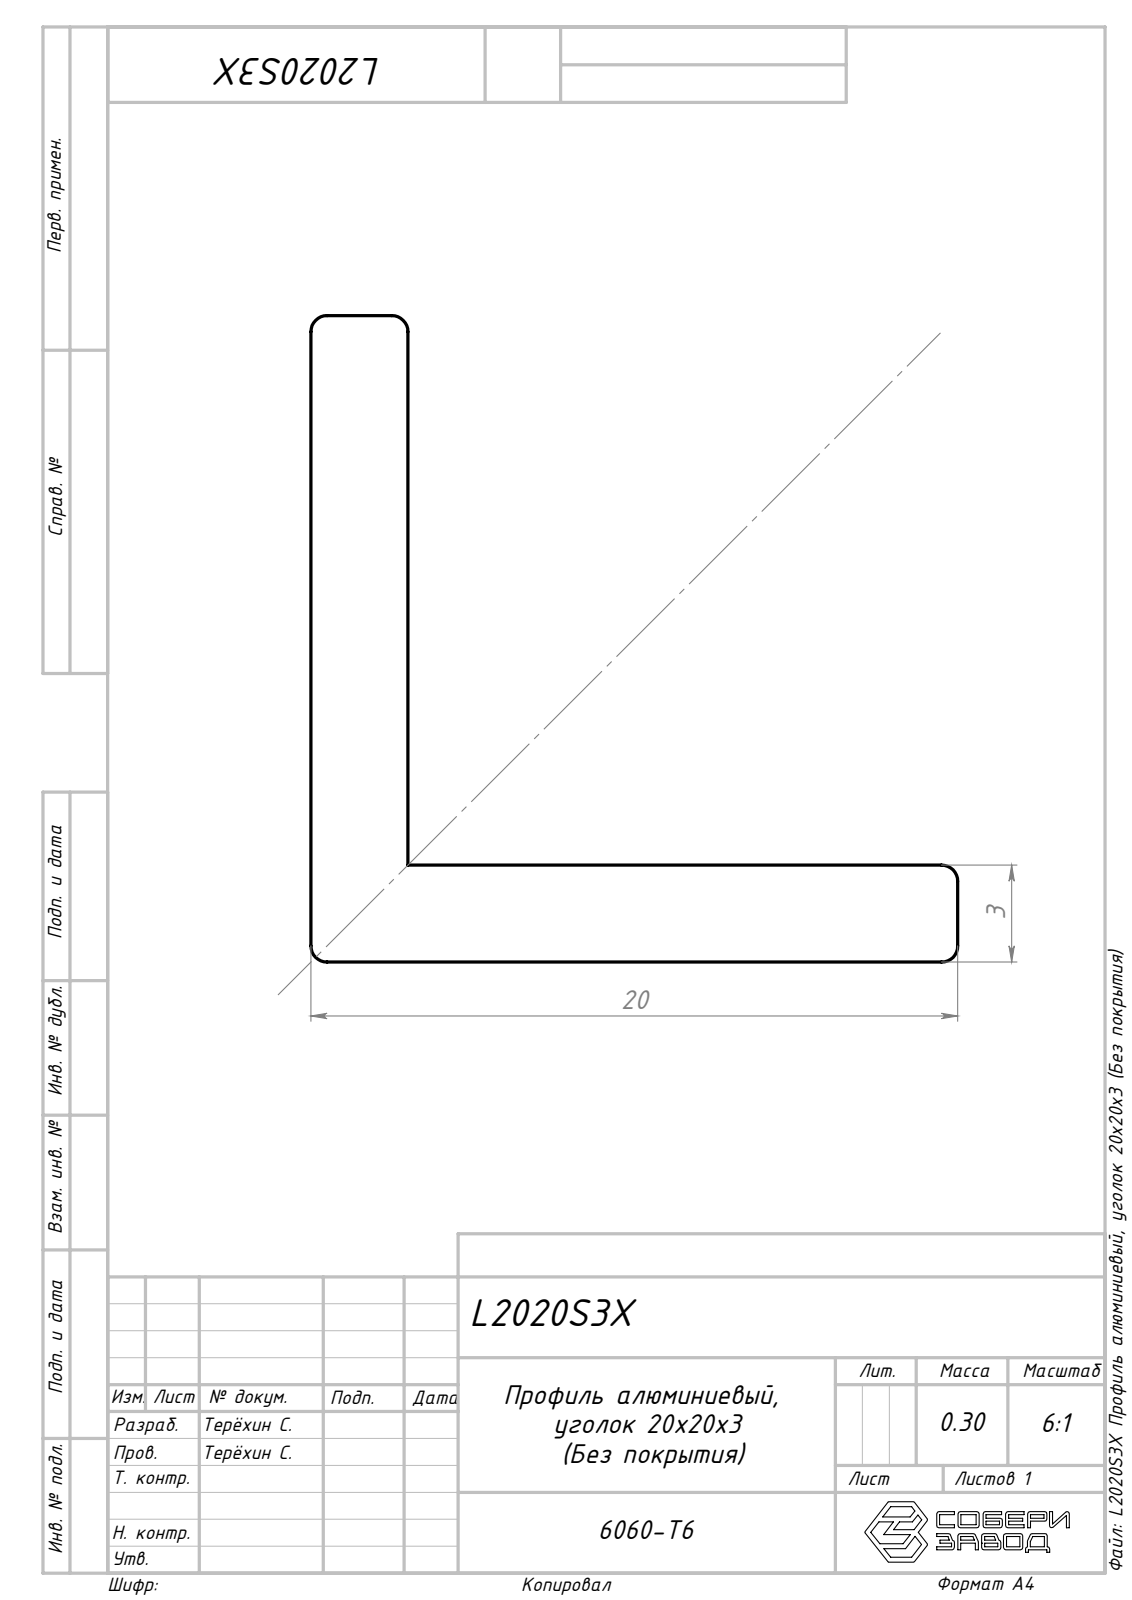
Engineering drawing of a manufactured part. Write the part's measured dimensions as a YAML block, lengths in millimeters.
part_name: "Сборка6; L2020S3X Профиль алюминиевый, уголок 20x20x3 (Без покрытия)_00"
step_written_by: "SolidWorks 2024 (AUTOMOTIVE_DESIGN)"
units: millimeters
bodies: {solids: 1, faces: 13, planar: 8, cylindrical: 5, other: 0}
overall_size: [1000, 20, 20]
volume: 110732
surface_area: 79148
partial_cylinders:
  - {radius: 0.5, count: 5}
face_to_face_distances: [3, 20, 17, 1000]
